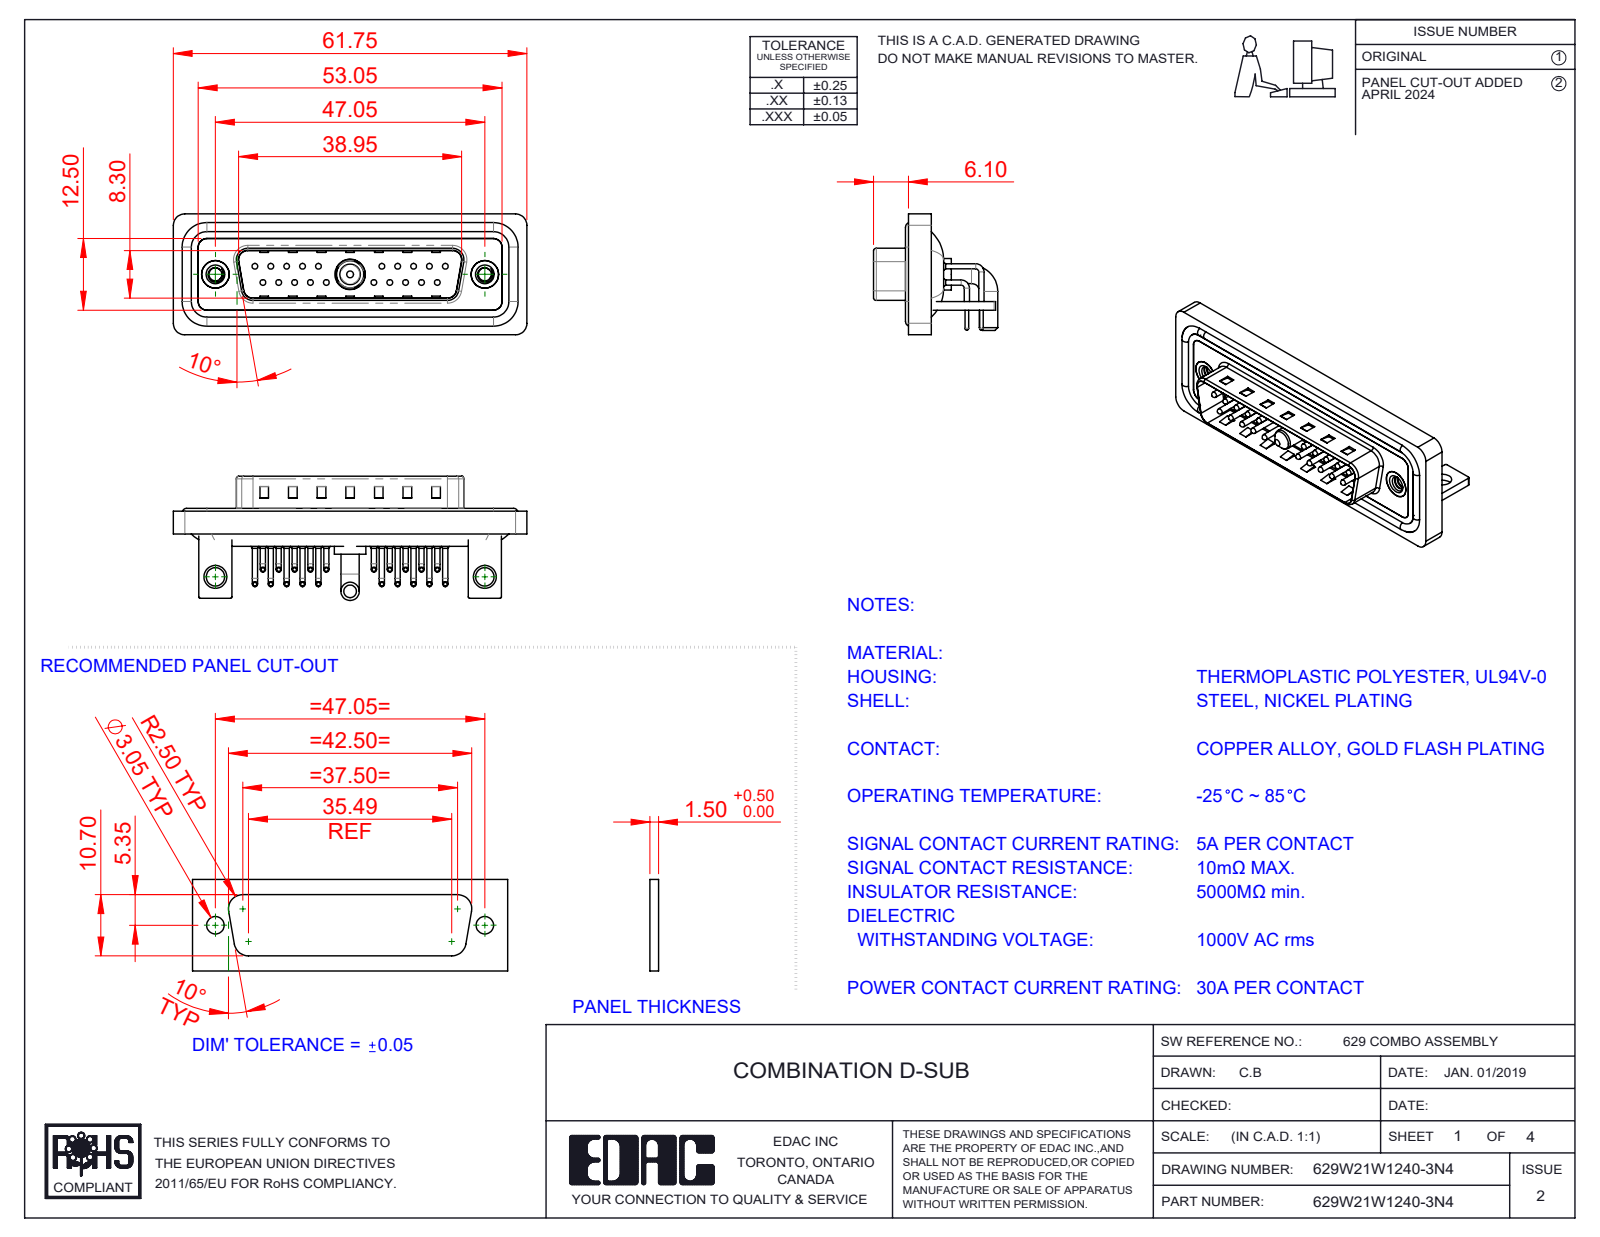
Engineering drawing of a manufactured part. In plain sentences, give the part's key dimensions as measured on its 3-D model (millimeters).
The part is named "629Combo Contact Row 1; 629W21W1140-3N4; 629Combo Housing_21W1; 629Combo Waterproof Housing_25 Contacts (+6 more)". Its 3-D file was written by "SolidWorks 2023 (CONFIG_CONTROL_DESIGN)". It is 31 solids with 2766 faces: 1519 planar, 947 cylindrical and 300 other. Overall it measures 61.75 by 21.7 by 21.1 millimeters. Its volume is 7 724 cubic millimeters and its surface area 13 326 square millimeters. Round holes: 20 of diameter 0.75, 20 of diameter 1.6, 20 of diameter 2, 2 of diameter 2.26, 2 of diameter 3.2, 2 of diameter 4, 2 of diameter 4.8, 2 of diameter 5, 1 of diameter 4.85, 1 of diameter 5.3. Round bosses or shafts: 40 of diameter 0.9, 20 of diameter 1.5, 20 of diameter 1, 20 of diameter 0.65, 4 of diameter 1.6, 2 of diameter 4.9, 2 of diameter 3.2, 1 of diameter 5.5. Partial cylindrical surfaces (rounded edges, fillets, slot ends): 20 of radius 1.01, 19 of radius 2, 18 of radius 1.5, 16 of radius 0.25, 9 of radius 0.5, 8 of radius 1.6, 4 of radius 0.6, 4 of radius 0.65. The main face-to-face distances are 0.4, 0.8, 2.1, 2.9, 1.5, 1.1, 4.1, 1.6, 4.5, 3.7. The hole center spacings are 3.16, 2.77, 5.54, 8.31, 5.04, 19.39, 20.97, 22.16.
